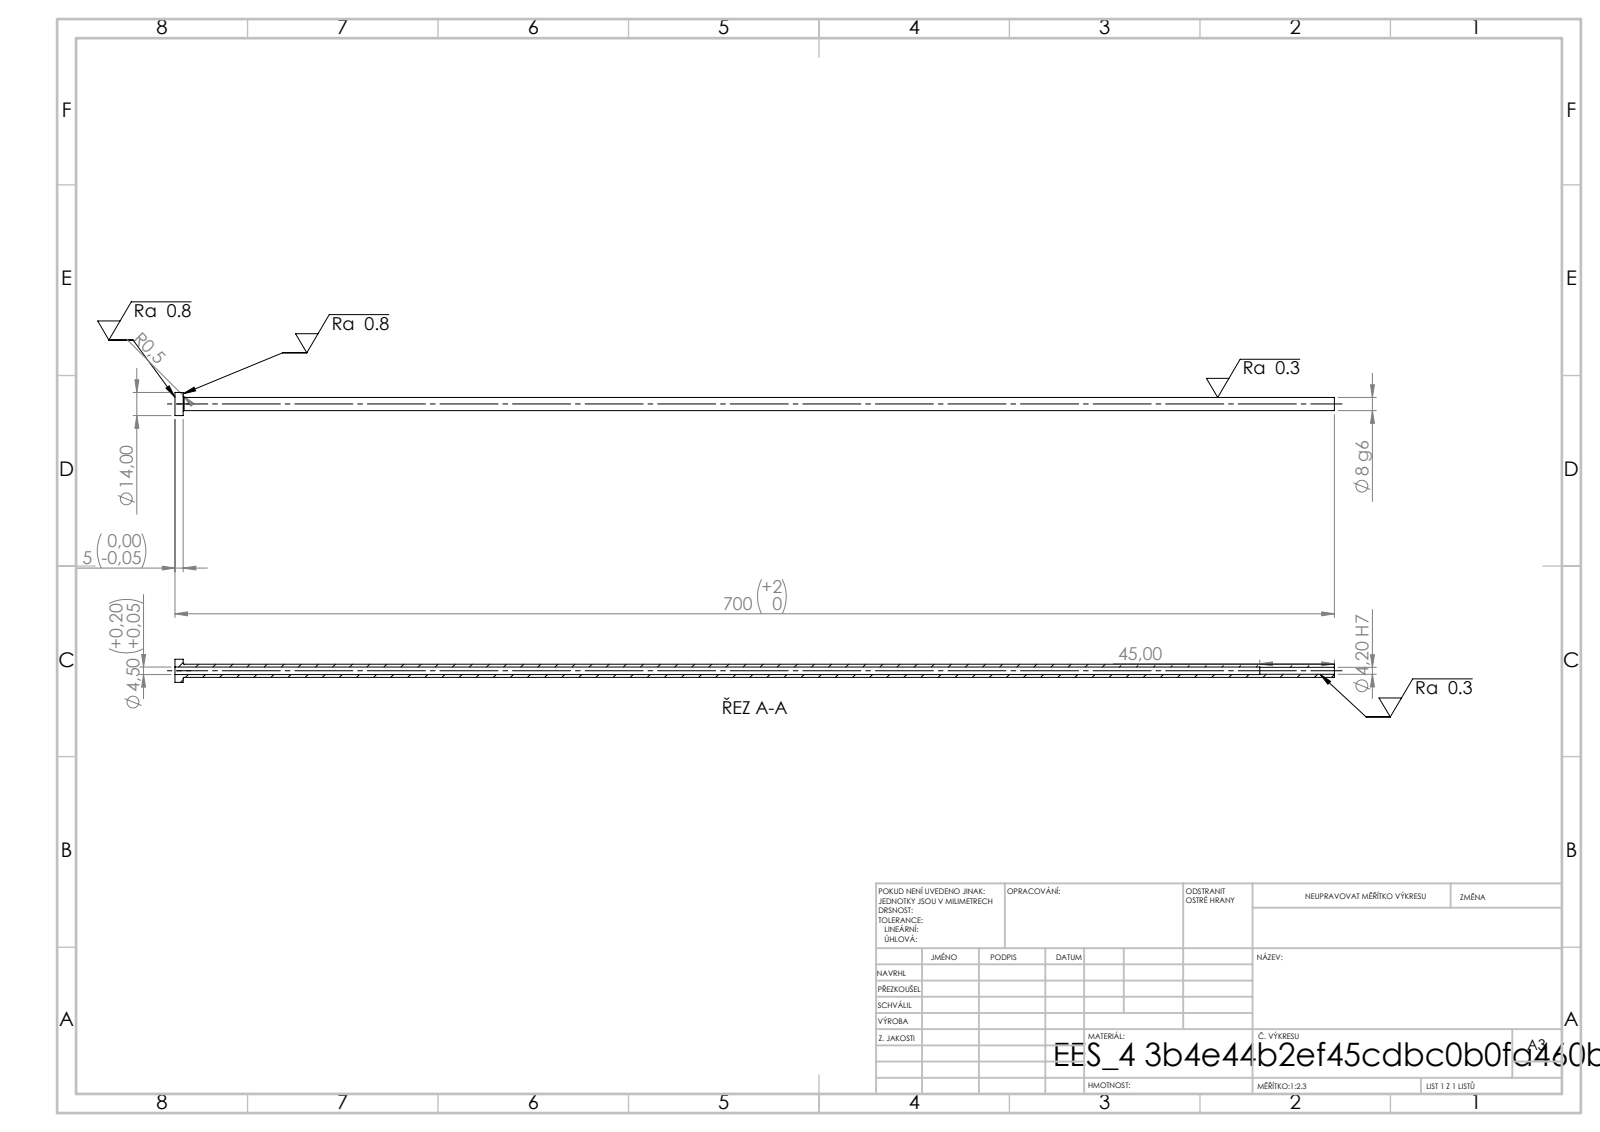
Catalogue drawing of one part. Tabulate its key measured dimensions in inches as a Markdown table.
| quantity | value |
| --- | --- |
| STEP written by | SolidWorks 2019 (CONFIG_CONTROL_DESIGN) |
| units | inches |
| bodies | 1 solid, 14 faces (4 planar, 8 cylindrical, 2 other) |
| overall size | 27.559 × 0.551 × 0.551 |
| volume | 1.505 in³ |
| surface area | 43.11 in² |
| round holes (diameter × count) | 0.165 × 1, 0.177 × 1 |
| round bosses / shafts (diameter × count) | 0.551 × 1, 0.315 × 1 |
| main face-to-face distances | 0.197, 27.559, 27.362, 25.787, 25.591, 1.772 |
